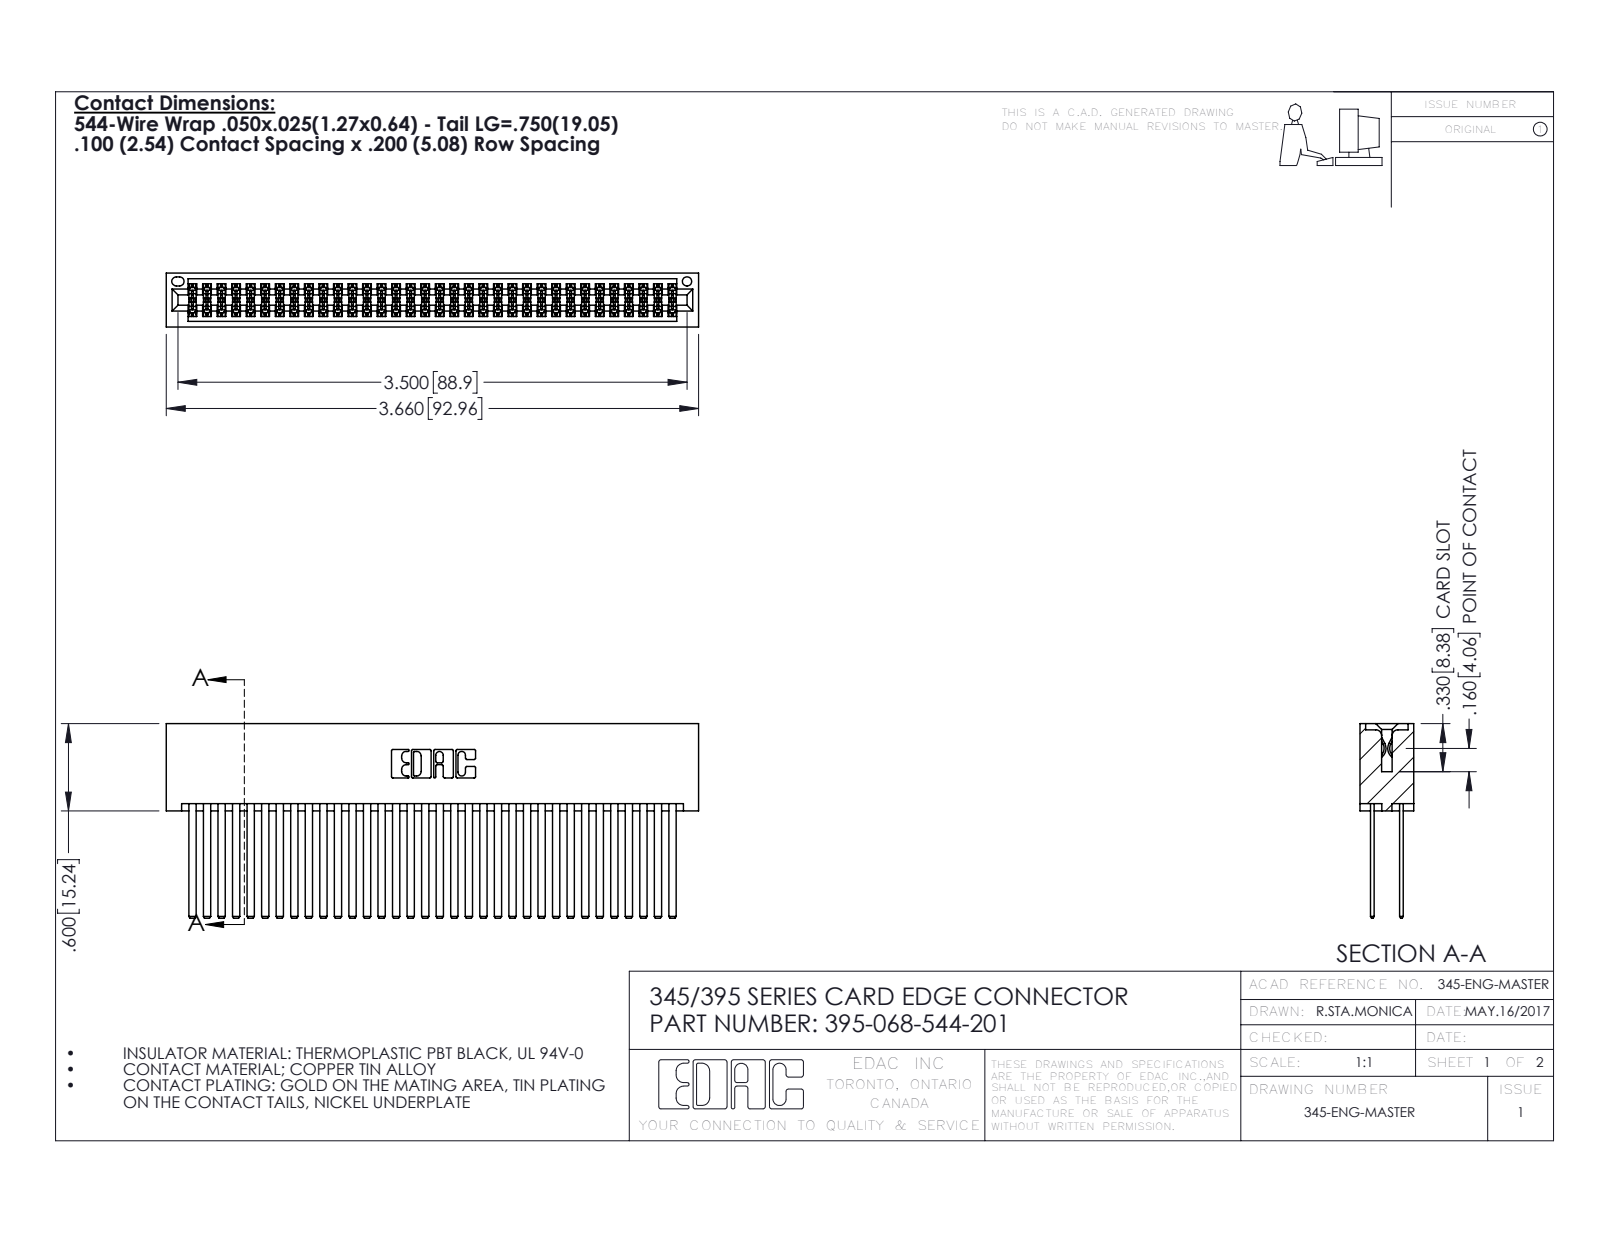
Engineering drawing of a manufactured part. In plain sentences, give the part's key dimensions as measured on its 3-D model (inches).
The part is named "395-068-544-201; 345-292-001_345-293-144; 345 Part_No Mounting Lugs". Its 3-D file was written by "SolidWorks 2016 (CONFIG_CONTROL_DESIGN)". It is 69 solids with 3110 faces: 2048 planar, 1062 cylindrical and 0 other. Overall it measures 3.66 by 1.337 by 0.37 inches. Its volume is 0.642 cubic inches and its surface area 28.68 square inches. Round holes: 1 of diameter 0.064. Partial cylindrical surfaces (rounded edges, fillets, slot ends): 102 of radius 0.006, 22 of radius 0.01, 6 of radius 0.007, 6 of radius 0.031, 3 of radius 0.026, 2 of radius 0.014, 2 of radius 0.019, 2 of radius 0.022. The main face-to-face distances are 0.2, 0.025, 0.298, 0.072, 0.098, 0.272, 0.225, 0.175, 0.37, 0.05.
